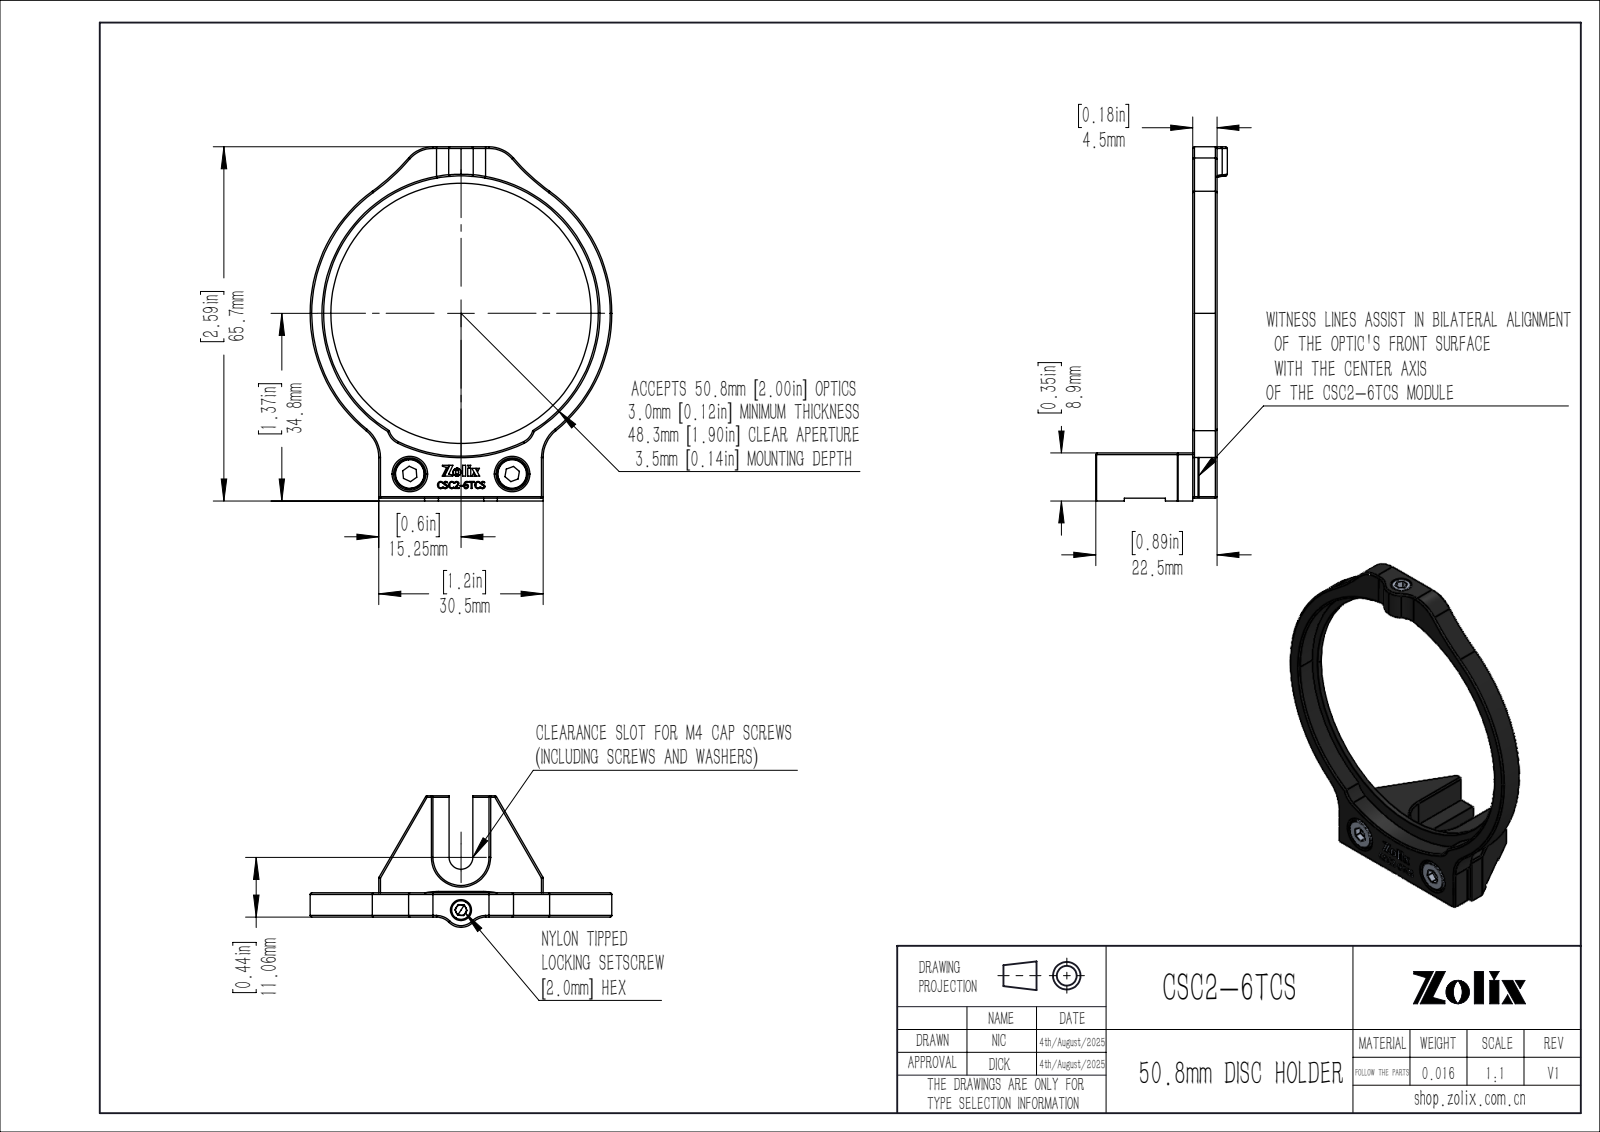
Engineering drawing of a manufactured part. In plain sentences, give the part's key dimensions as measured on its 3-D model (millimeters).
The part is named "CSC2-6TCS". Its 3-D file was written by "SolidWorks 2020 (CONFIG_CONTROL_DESIGN)". It is 5 solids with 530 faces: 269 planar, 89 cylindrical and 172 other. Overall it measures 65.7 by 56 by 24.4 millimeters. Its volume is 5 933 cubic millimeters and its surface area 5 827 square millimeters. Round holes: 2 of diameter 1.6, 2 of diameter 2.5, 2 of diameter 3.4, 2 of diameter 6, 1 of diameter 3.3, 1 of diameter 48.3, 1 of diameter 51. Round bosses or shafts: 2 of diameter 5.5, 2 of diameter 3, 1 of diameter 4, 1 of diameter 2.5. Partial cylindrical surfaces (rounded edges, fillets, slot ends): 24 of radius 0.3, 5 of radius 3.2, 2 of radius 0.8, 2 of radius 6, 2 of radius 6.4, 2 of radius 13.1, 2 of radius 40, 1 of radius 2.2. The main face-to-face distances are 4.5, 0.5, 1, 3.5, 8.4, 8.9, 3, 3.4, 3.9, 5. The hole center spacings are 6.96, 12.75, 31.28, 32.44, 6, 19.
